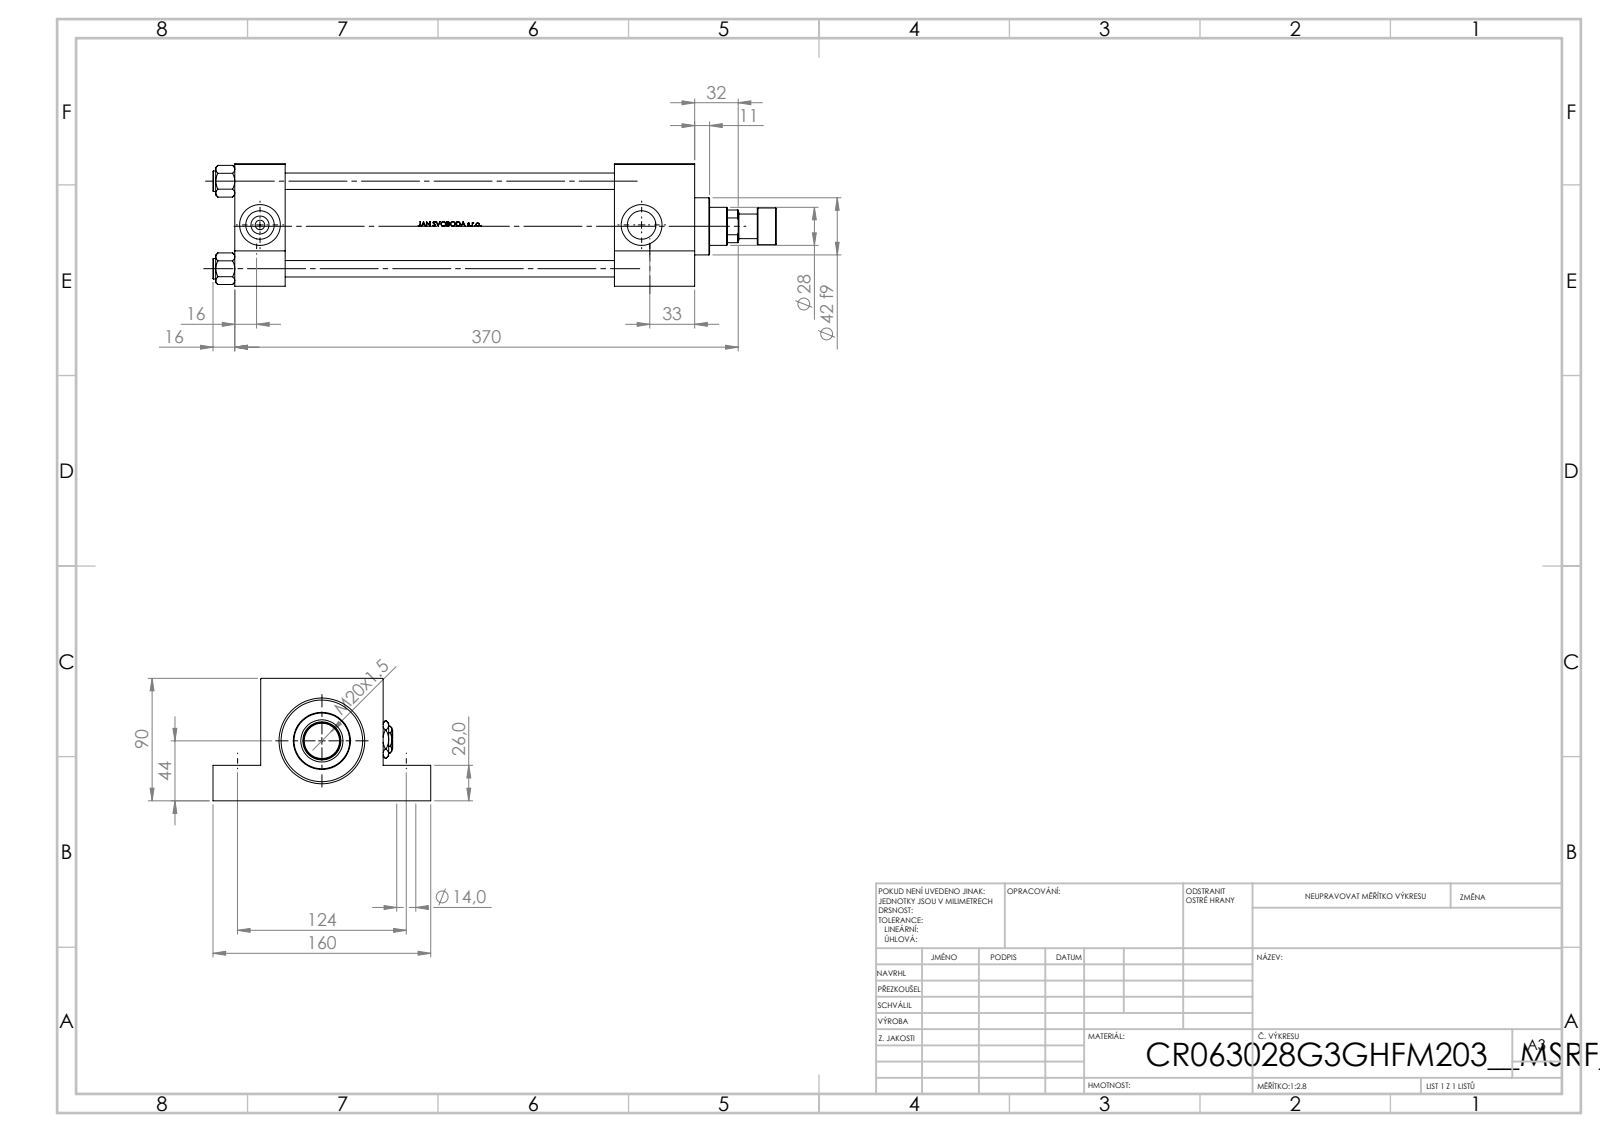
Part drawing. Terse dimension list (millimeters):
name: V215CR_VCP_G; Zatka_pro_OIL_PORT; V215CR_ROD_END_F; V215CR_G_TYCINKA (+3 more)
written by: SolidWorks 2019 (CONFIG_CONTROL_DESIGN)
unit: mm
bodies: 14 solids, 1198 faces (482 planar, 136 cylindrical, 580 other)
size: 414 × 160 × 90
volume: 1 431 000 mm³; area: 327 164 mm²
holes: 4× ⌀12, 4× ⌀14, 2× ⌀7, 2× ⌀20.96, 2× ⌀30, 1× ⌀18.5, 1× ⌀28, 1× ⌀31, 1× ⌀50, 1× ⌀60, 1× ⌀63
bosses: 4× ⌀15, 1× ⌀69, 1× ⌀42, 1× ⌀27, 1× ⌀18
face distances: 90, 37, 301, 338, 59, 279, 242, 64, 26, 35
hole spacings: 64.3, 44.77, 46.18, 90.93, 124, 289, 314.48, 280.5
